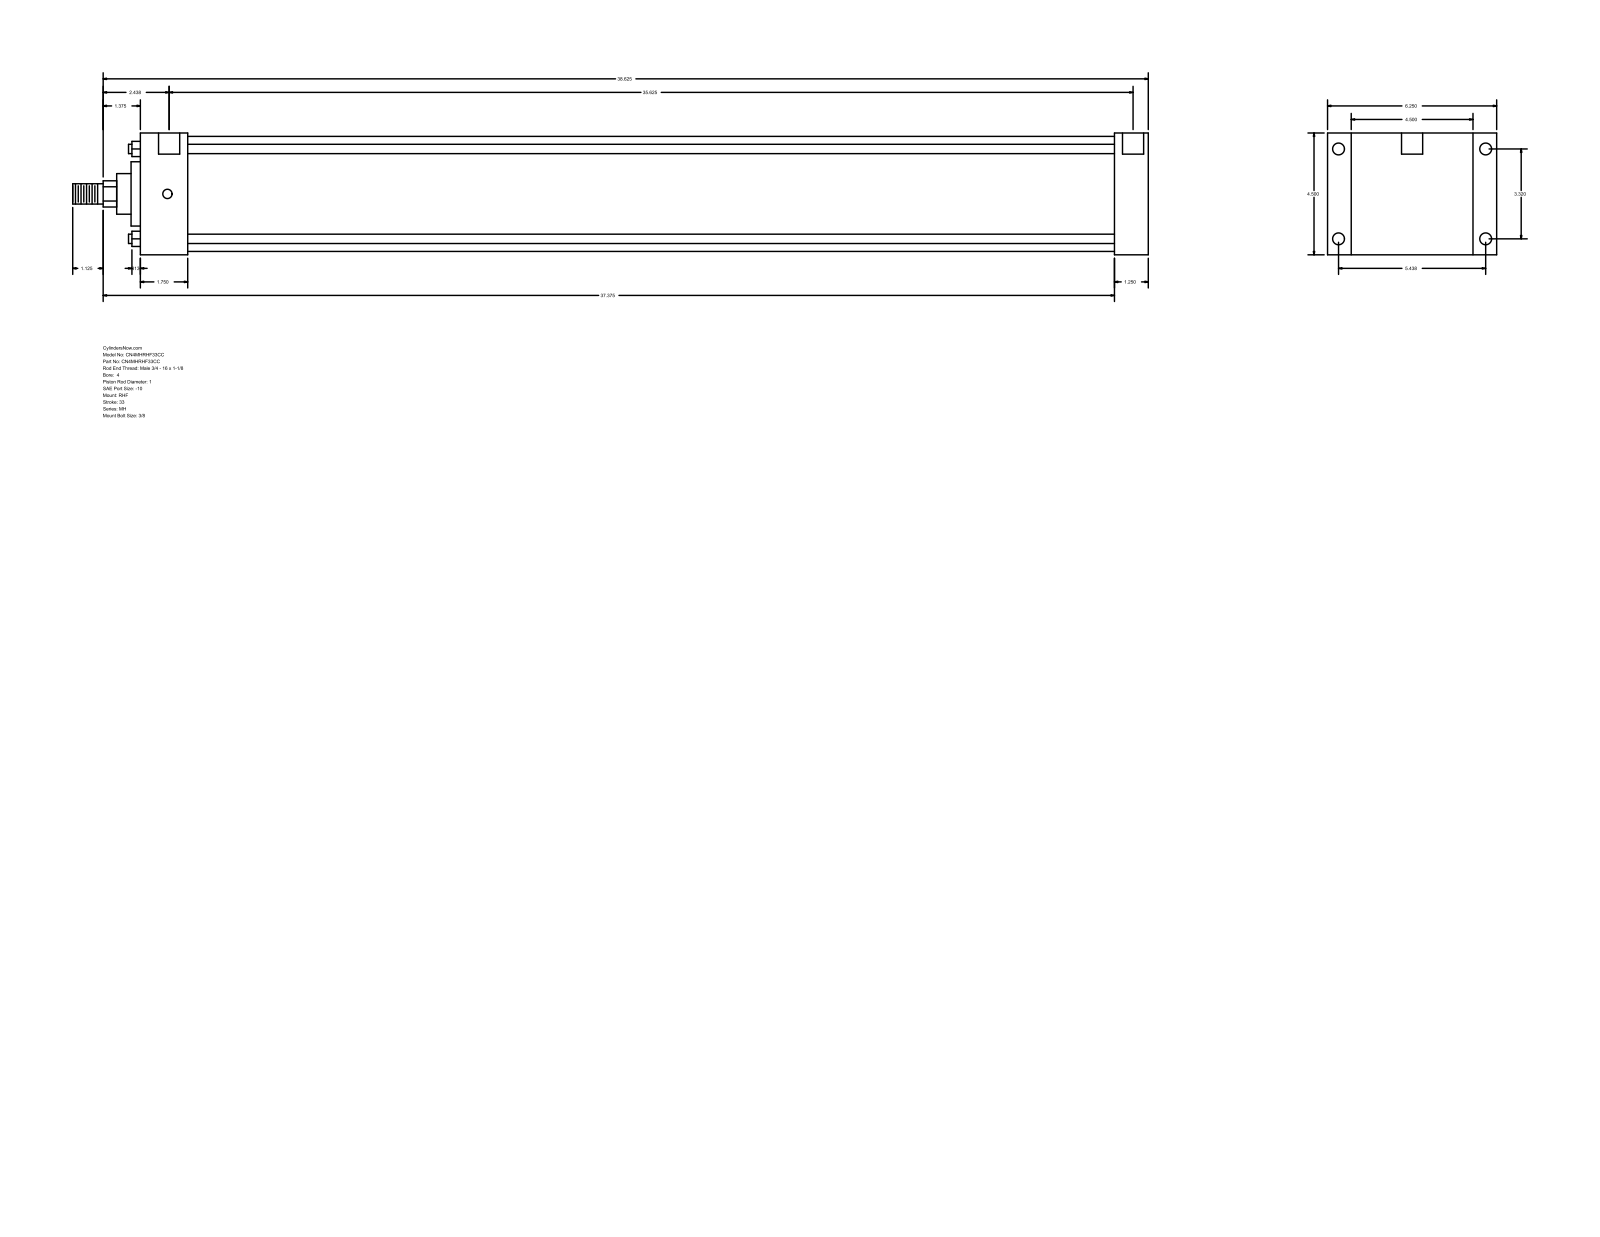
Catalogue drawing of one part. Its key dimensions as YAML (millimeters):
part_name: "MH_RHF__0400_1"
step_written_by: "GSSL Pune (CONFIG_CONTROL_DESIGN)"
units: millimeters
bodies: {solids: 0, faces: 90, planar: 61, cylindrical: 29, other: 0}
overall_size: [1009.65, 158.75, 114.3]
round_holes:
  - {diameter: 8.73, count: 4}
  - {diameter: 11.13, count: 4}
  - {diameter: 19.84, count: 2}
round_bosses_or_shafts:
  - {diameter: 8.76, count: 4}
  - {diameter: 107.95, count: 1}
  - {diameter: 60.33, count: 1}
  - {diameter: 38.1, count: 1}
  - {diameter: 25.4, count: 1}
  - {diameter: 19.05, count: 1}
partial_cylinders:
  - {radius: 12.29, count: 1}
face_to_face_distances: [114.3, 946.16, 914.41, 31.75, 22.23, 136.53, 44.46, 869.95, 901.7, 158.76]
hole_center_spacings: [84.32, 138.12, 161.82, 908.05, 1.58, 1.59, 904.88, 906.46]
